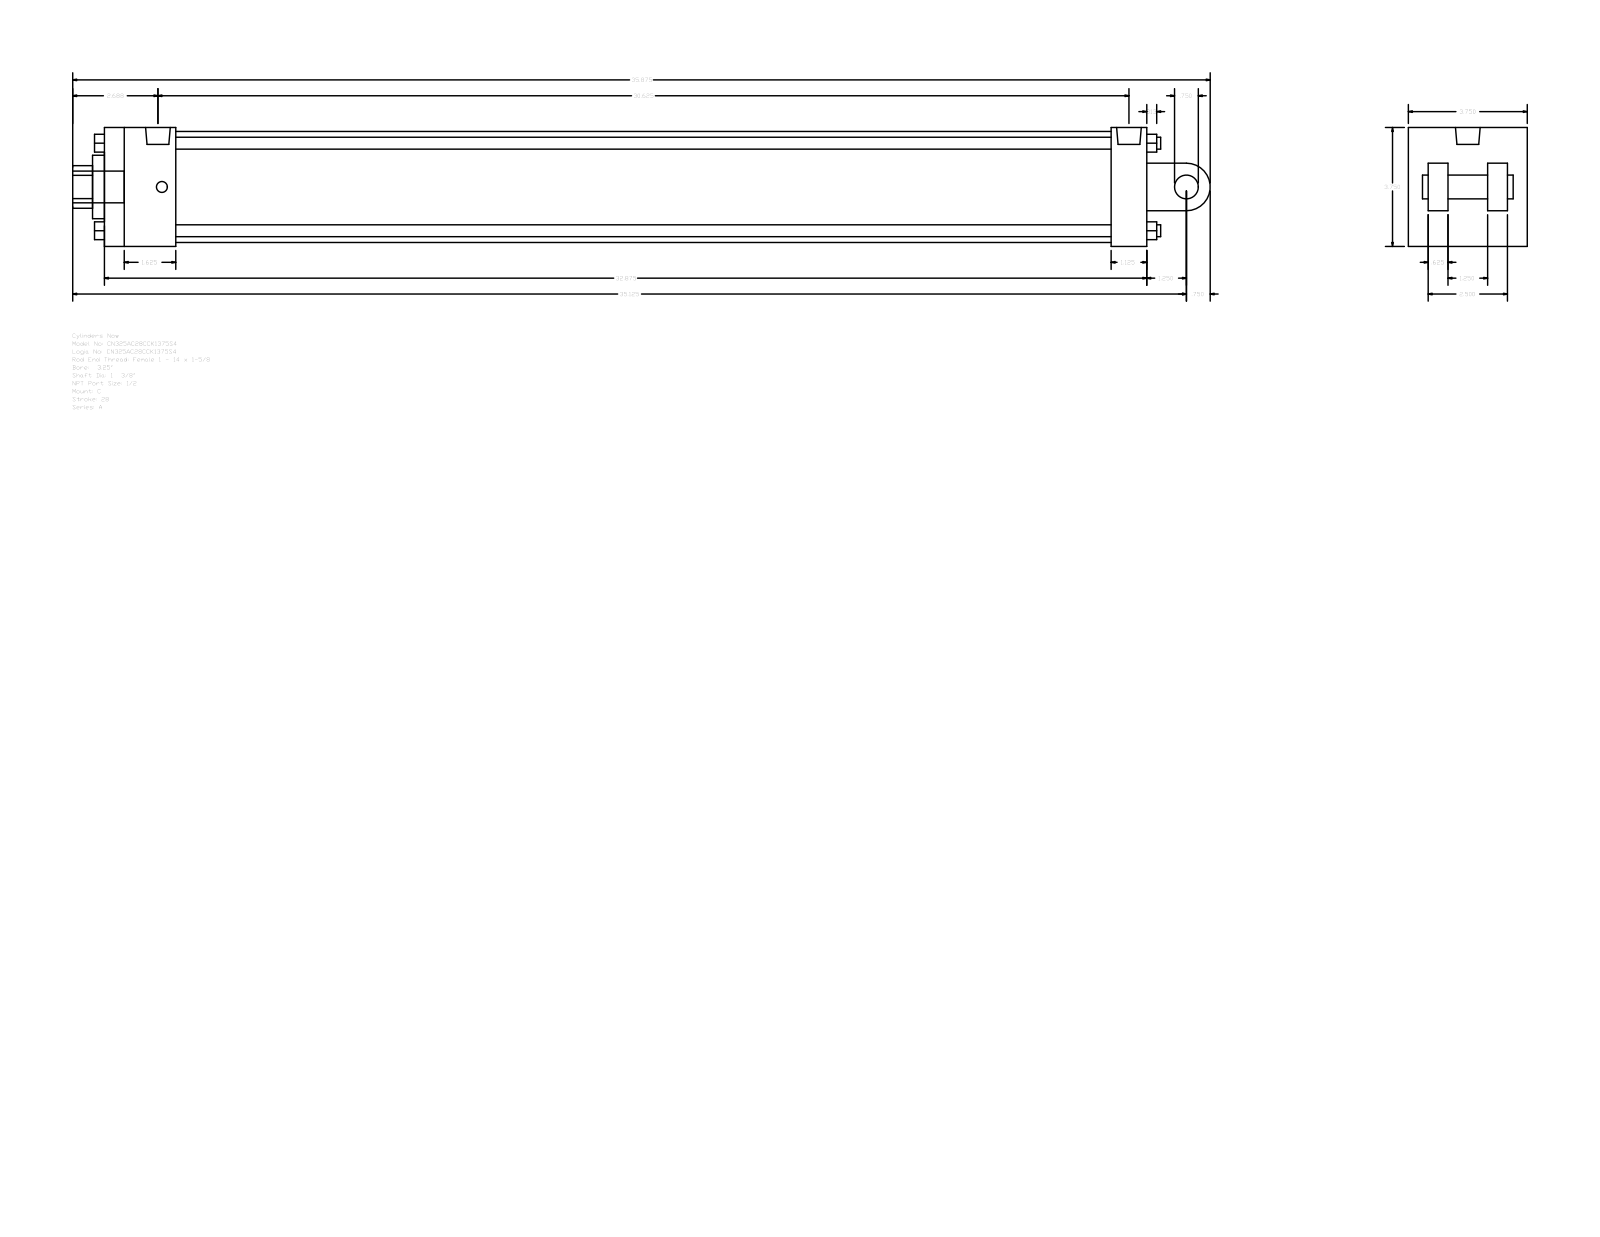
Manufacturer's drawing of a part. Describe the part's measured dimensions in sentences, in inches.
The part is named "A_C__0325_1.375". Its 3-D file was written by "GSSL Pune (CONFIG_CONTROL_DESIGN)". It is 0 solids with 135 faces: 102 planar, 33 cylindrical and 0 other. Overall it measures 35.875 by 3.75 by 3.75 inches. Round holes: 2 of diameter 0.344, 1 of diameter 0.778, 1 of diameter 1.375, 1 of diameter 2, 1 of diameter 3.5. Round bosses or shafts: 4 of diameter 0.375, 2 of diameter 0.344, 1 of diameter 1, 1 of diameter 0.778, 1 of diameter 0.75. Partial cylindrical surfaces (rounded edges, fillets, slot ends): 1 of radius 0.672, 1 of radius 0.75. The main face-to-face distances are 3.75, 0.625, 32.875, 1.125, 2.5, 2.625, 1.25, 3.125, 1.875, 31.75. The hole center spacings are 0.125.
